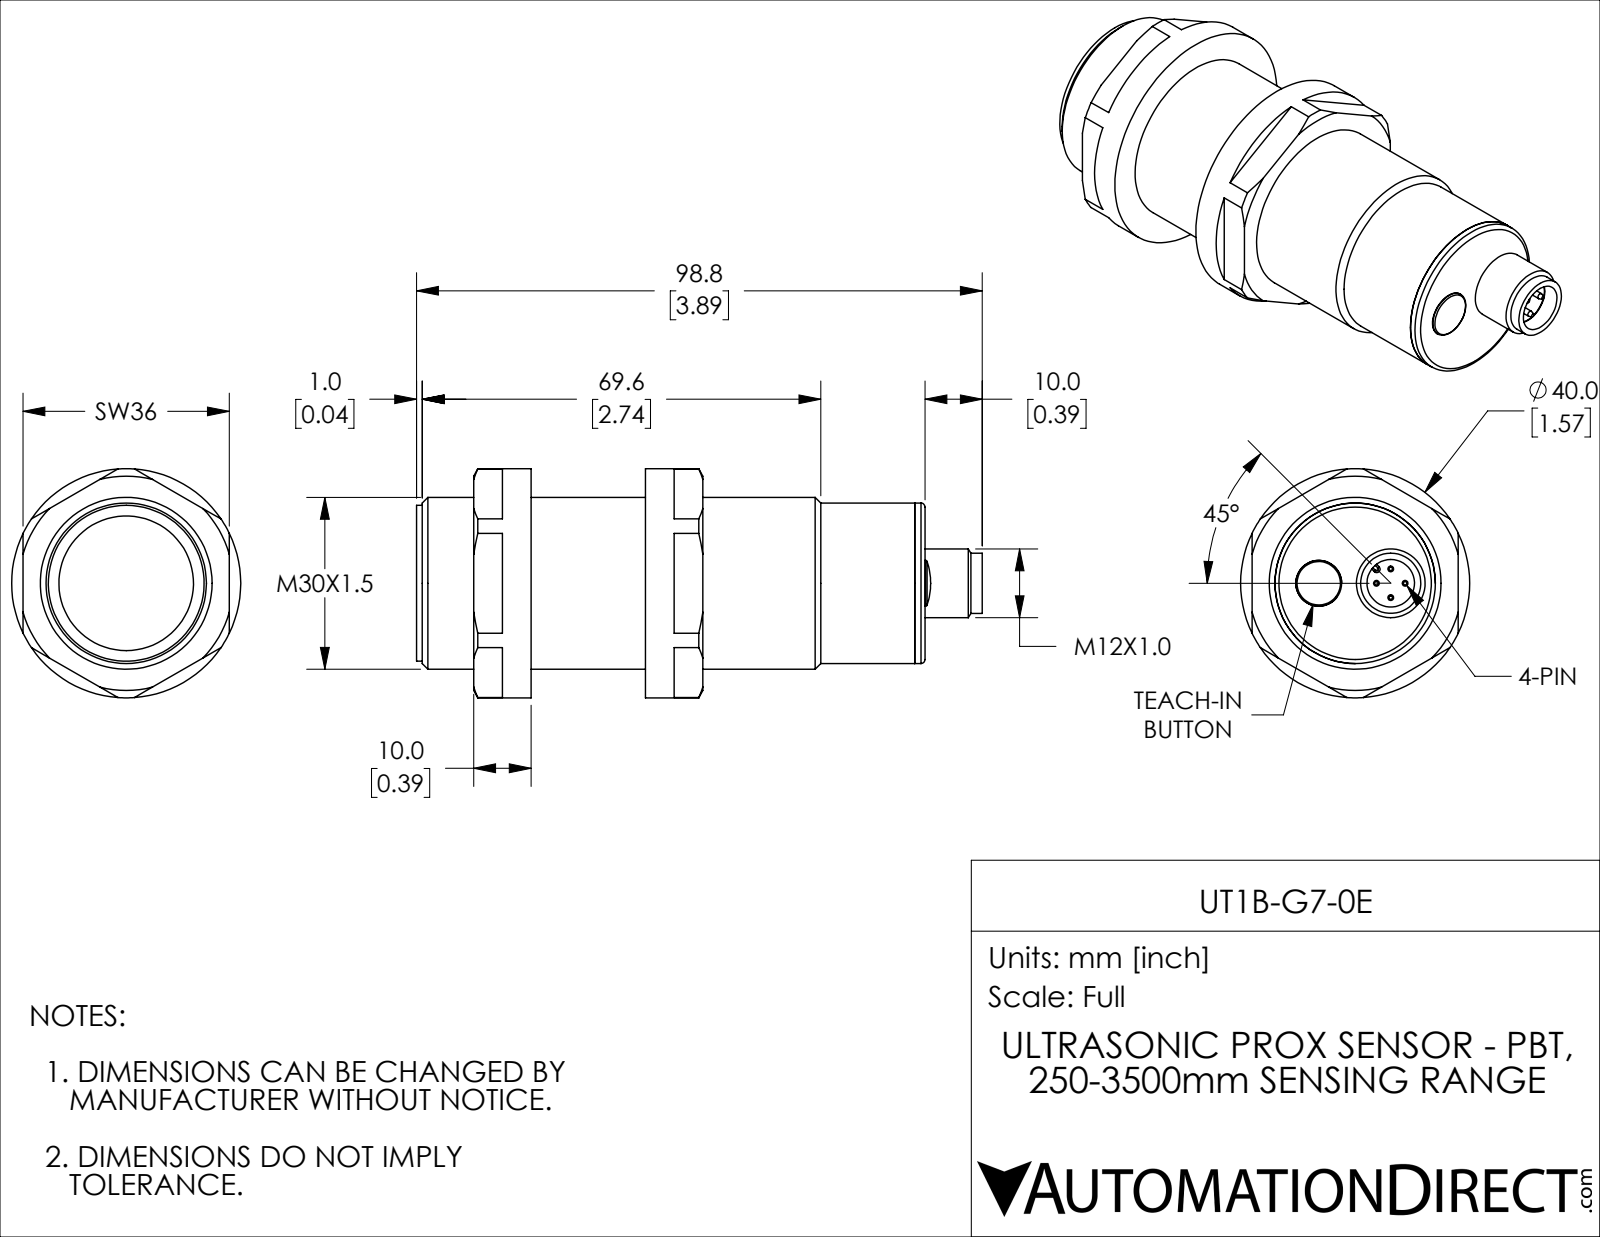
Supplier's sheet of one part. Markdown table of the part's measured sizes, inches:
| quantity | value |
| --- | --- |
| part name | UT1B-G7-0E |
| STEP written by | SolidWorks 2018 (AUTOMOTIVE_DESIGN) |
| units | inches |
| bodies | 7 solids, 158 faces (58 planar, 53 cylindrical, 47 other) |
| overall size | 3.89 × 1.575 × 1.575 |
| volume | 4.337 in³ |
| surface area | 30.82 in² |
| round holes (diameter × count) | 0.071 × 4, 0.315 × 1, 0.327 × 1, 0.372 × 1, 0.925 × 1, 1.181 × 1 |
| round bosses / shafts (diameter × count) | 0.039 × 4, 1.575 × 1, 1.102 × 1, 1.071 × 1, 0.472 × 1, 0.413 × 1, 0.364 × 1 |
| partial cylindrical surfaces (radius × count) | 0.012 × 2, 0.024 × 1 |
| main face-to-face distances | 3.386, 0.394, 1.181, 0.787, 0.197, 1.575, 1.85, 1.535, 0.748, 2.638 |
| hole center spacings | 0.098, 0.139, 0.197, 0.264, 0.505, 0.146, 0.245, 0.25 |
